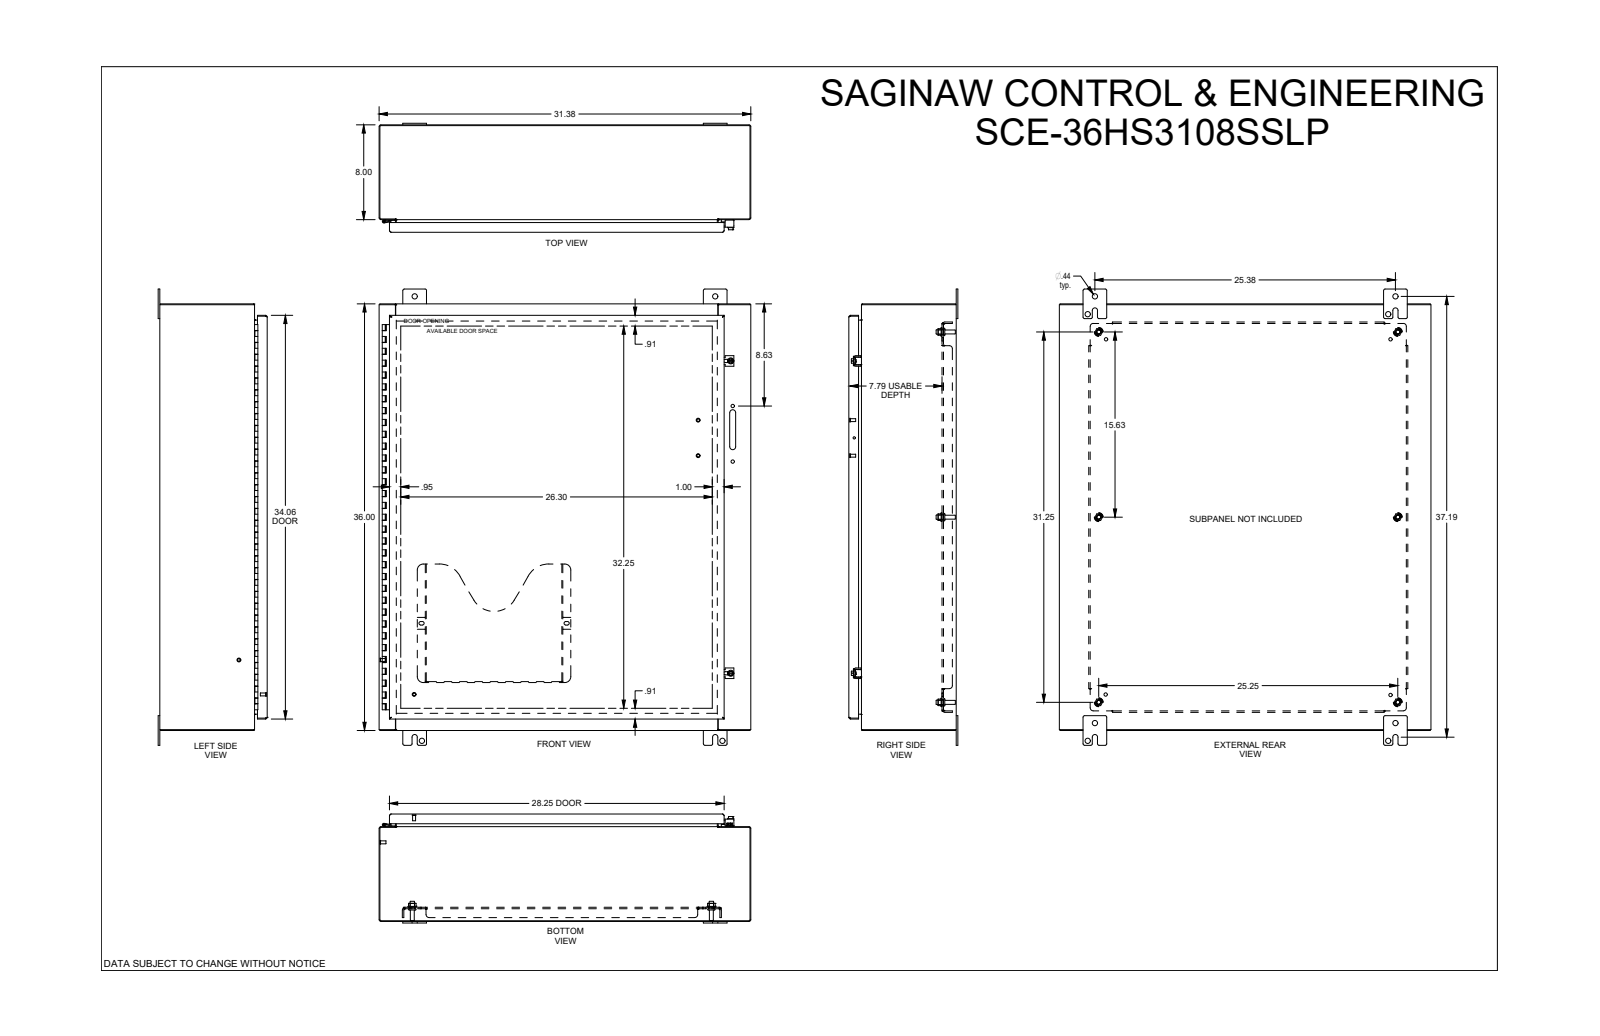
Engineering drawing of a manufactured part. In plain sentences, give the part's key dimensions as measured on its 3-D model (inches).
The part is named "SCE-36HS3108LP". Its 3-D file was written by "SolidWorks 2021 (AUTOMOTIVE_DESIGN)". It is 63 solids with 3240 faces: 1151 planar, 807 cylindrical and 1282 other. Overall it measures 38.5 by 31.375 by 9.343 inches. Its volume is 428.3 cubic inches and its surface area 9 749 square inches. Round holes: 6 of diameter 0.281, 6 of diameter 0.312, 6 of diameter 0.367, 6 of diameter 0.5, 4 of diameter 0.172, 4 of diameter 0.205, 4 of diameter 0.244, 4 of diameter 0.25, 4 of diameter 0.31, 4 of diameter 0.375, 2 of diameter 0.04, 2 of diameter 0.203. Round bosses or shafts: 8 of diameter 0.248, 6 of diameter 0.366, 6 of diameter 0.332, 6 of diameter 0.25, 6 of diameter 0.17, 4 of diameter 0.59, 4 of diameter 0.563, 4 of diameter 0.376. Partial cylindrical surfaces (rounded edges, fillets, slot ends): 119 of radius 0.01, 72 of radius 0.025, 24 of radius 0.029, 21 of radius 0.185, 20 of radius 0.015, 18 of radius 0.04, 12 of radius 0.043, 12 of radius 0.118. The main face-to-face distances are 0.075, 9.008, 8.933, 9.083, 0.125, 1.215, 1.14, 7.793, 7.868, 1.09. The hole center spacings are 15.625, 29.694, 1.375, 1.637, 2.282, 15.019, 17.251, 25.25.
